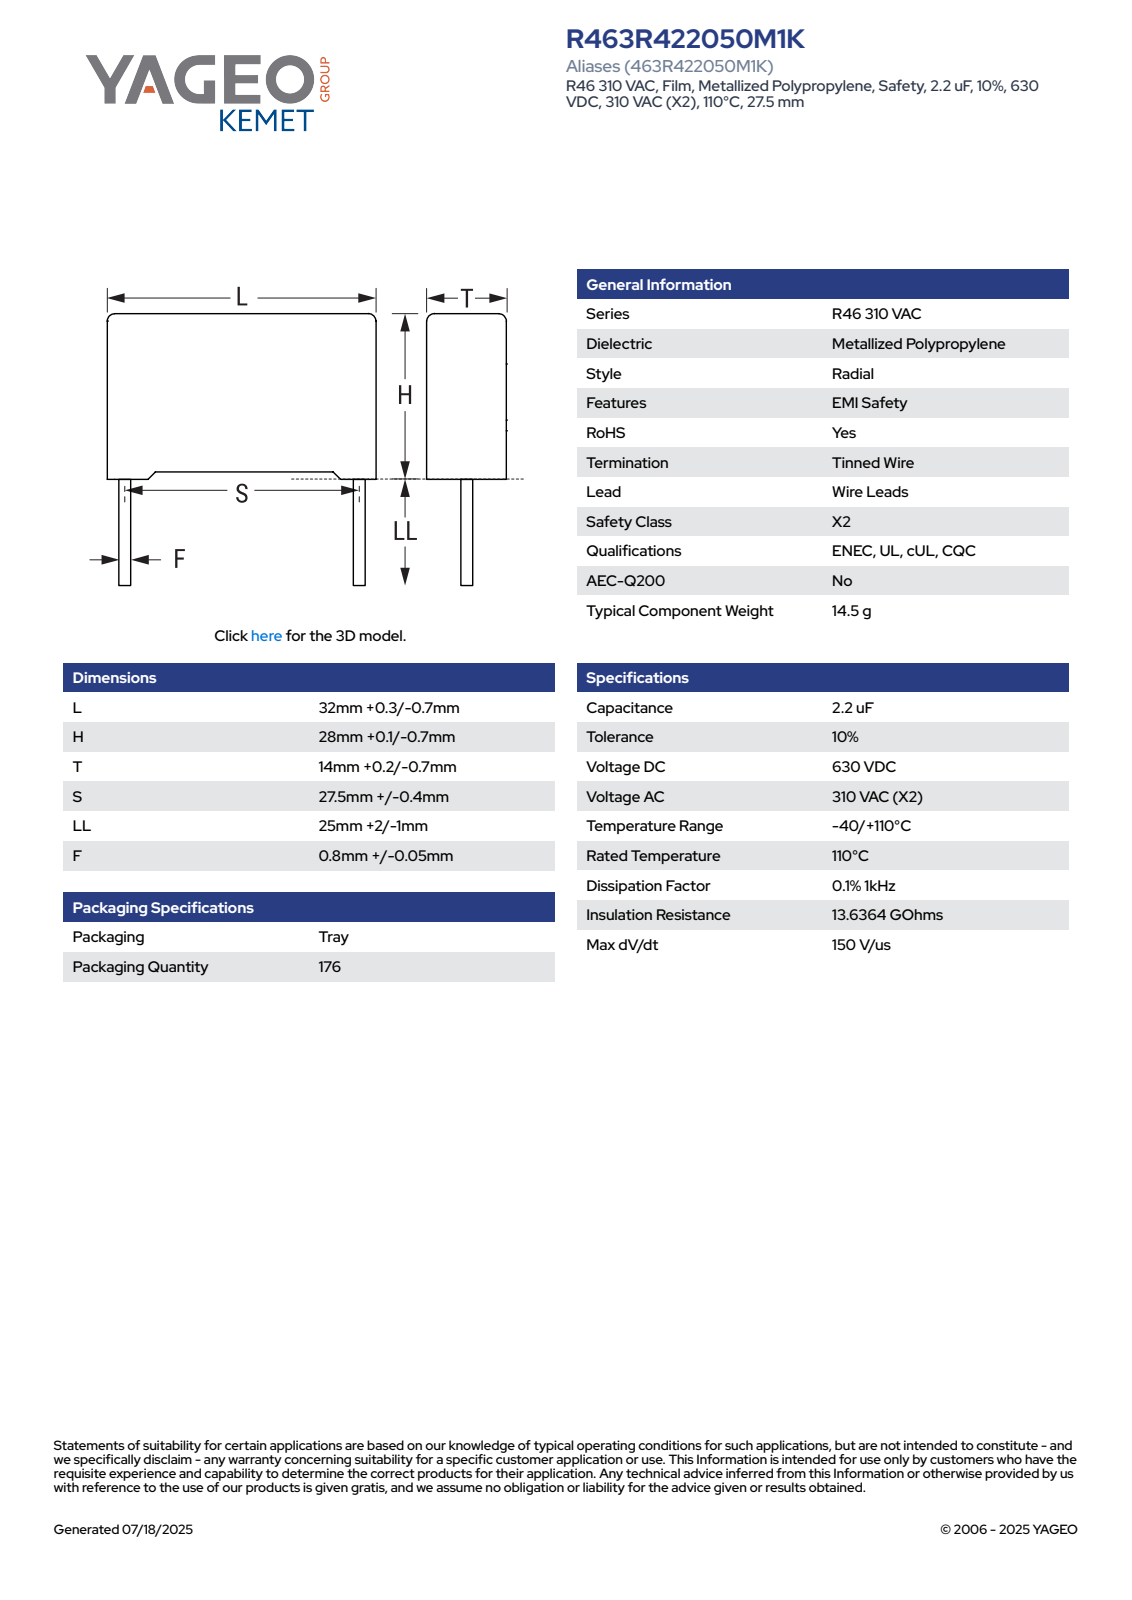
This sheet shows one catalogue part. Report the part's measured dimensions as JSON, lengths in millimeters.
{"part_name": "CFR_RB2_32X28X14_L32.3H28.1T14.2S27.5LL27F0.85", "step_written_by": "SolidWorks 2021 (AUTOMOTIVE_DESIGN)", "units": "millimeters", "bodies": {"solids": 4, "faces": 85, "planar": 77, "cylindrical": 8, "other": 0}, "overall_size": [55.1, 32.3, 14.21], "volume_mm3": 12533, "surface_area_mm2": 3723, "round_bosses_or_shafts": [[0.85, 2]], "partial_cylinders_radius": [[0.5, 4]], "face_to_face_distances": [14.2, 32.3, 27.13, 27.35, 0.75, 0.97, 28.1, 1.08, 31.22, 13.12]}
